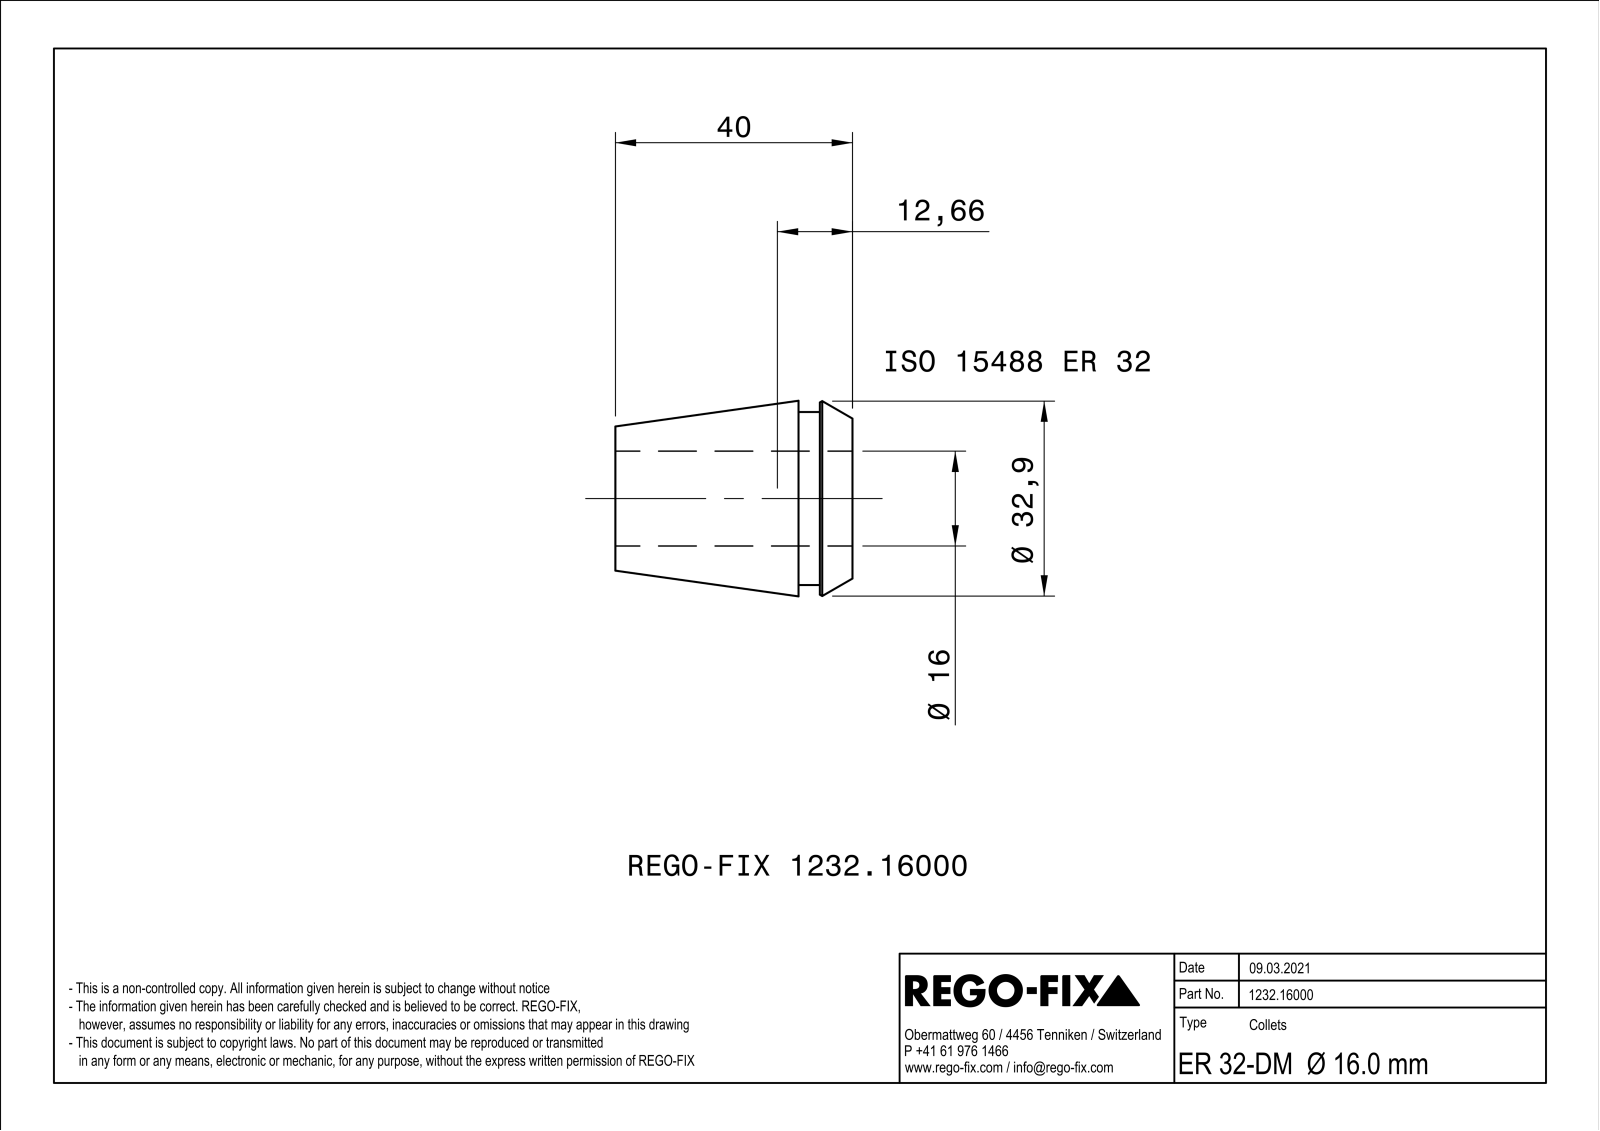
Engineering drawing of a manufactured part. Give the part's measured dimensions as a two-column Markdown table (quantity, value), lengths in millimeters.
| quantity | value |
| --- | --- |
| part name | NOCUT |
| STEP written by | SIEMENS PLM Software Solid Edge ST10 (AUTOMOTIVE_DESIGN) |
| units | millimeters |
| bodies | 1 solid, 154 faces (80 planar, 9 cylindrical, 65 other) |
| overall size | 40 × 32.98 × 32.98 |
| volume | 15 379 mm³ |
| surface area | 11 758 mm² |
| round holes (diameter × count) | 16 × 1 |
| round bosses / shafts (diameter × count) | 29.2 × 1 |
| main face-to-face distances | 1, 40, 9.1, 30.9, 5.5, 3.6, 34.5, 16, 10.5, 6.9 |
